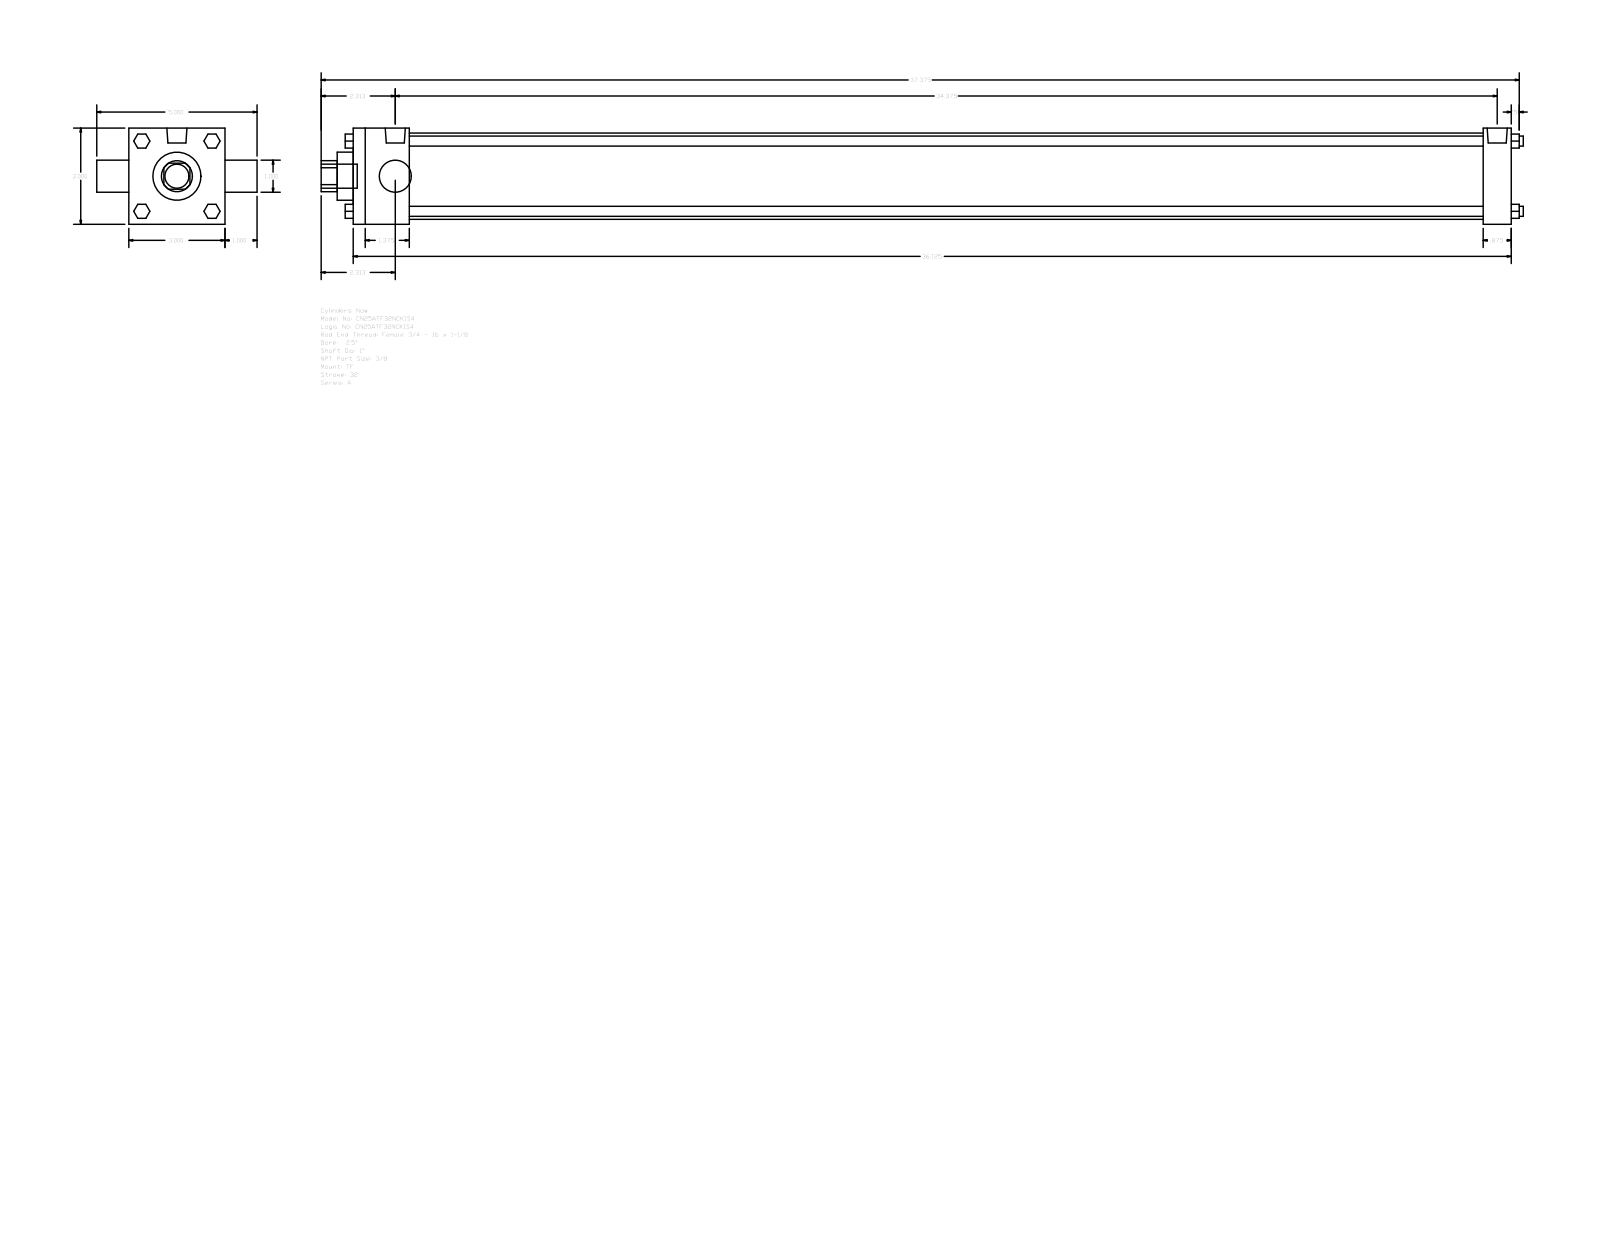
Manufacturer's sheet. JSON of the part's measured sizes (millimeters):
{"part_name": "A_TF__0250_1", "step_written_by": "GSSL Pune (CONFIG_CONTROL_DESIGN)", "units": "millimeters", "bodies": {"solids": 0, "faces": 120, "planar": 92, "cylindrical": 28, "other": 0}, "overall_size": [952.5, 127, 76.2], "round_holes": [[25.4, 2], [38.1, 1], [68.33, 1]], "round_bosses_or_shafts": [[7.94, 4], [5.56, 3], [15.93, 2], [19.05, 1]], "partial_cylinders_radius": [[12.29, 1]], "face_to_face_distances": [76.2, 917.58, 44.45, 895.35, 850.9, 873.13, 22.23, 25.4, 101.6, 930.28]}
